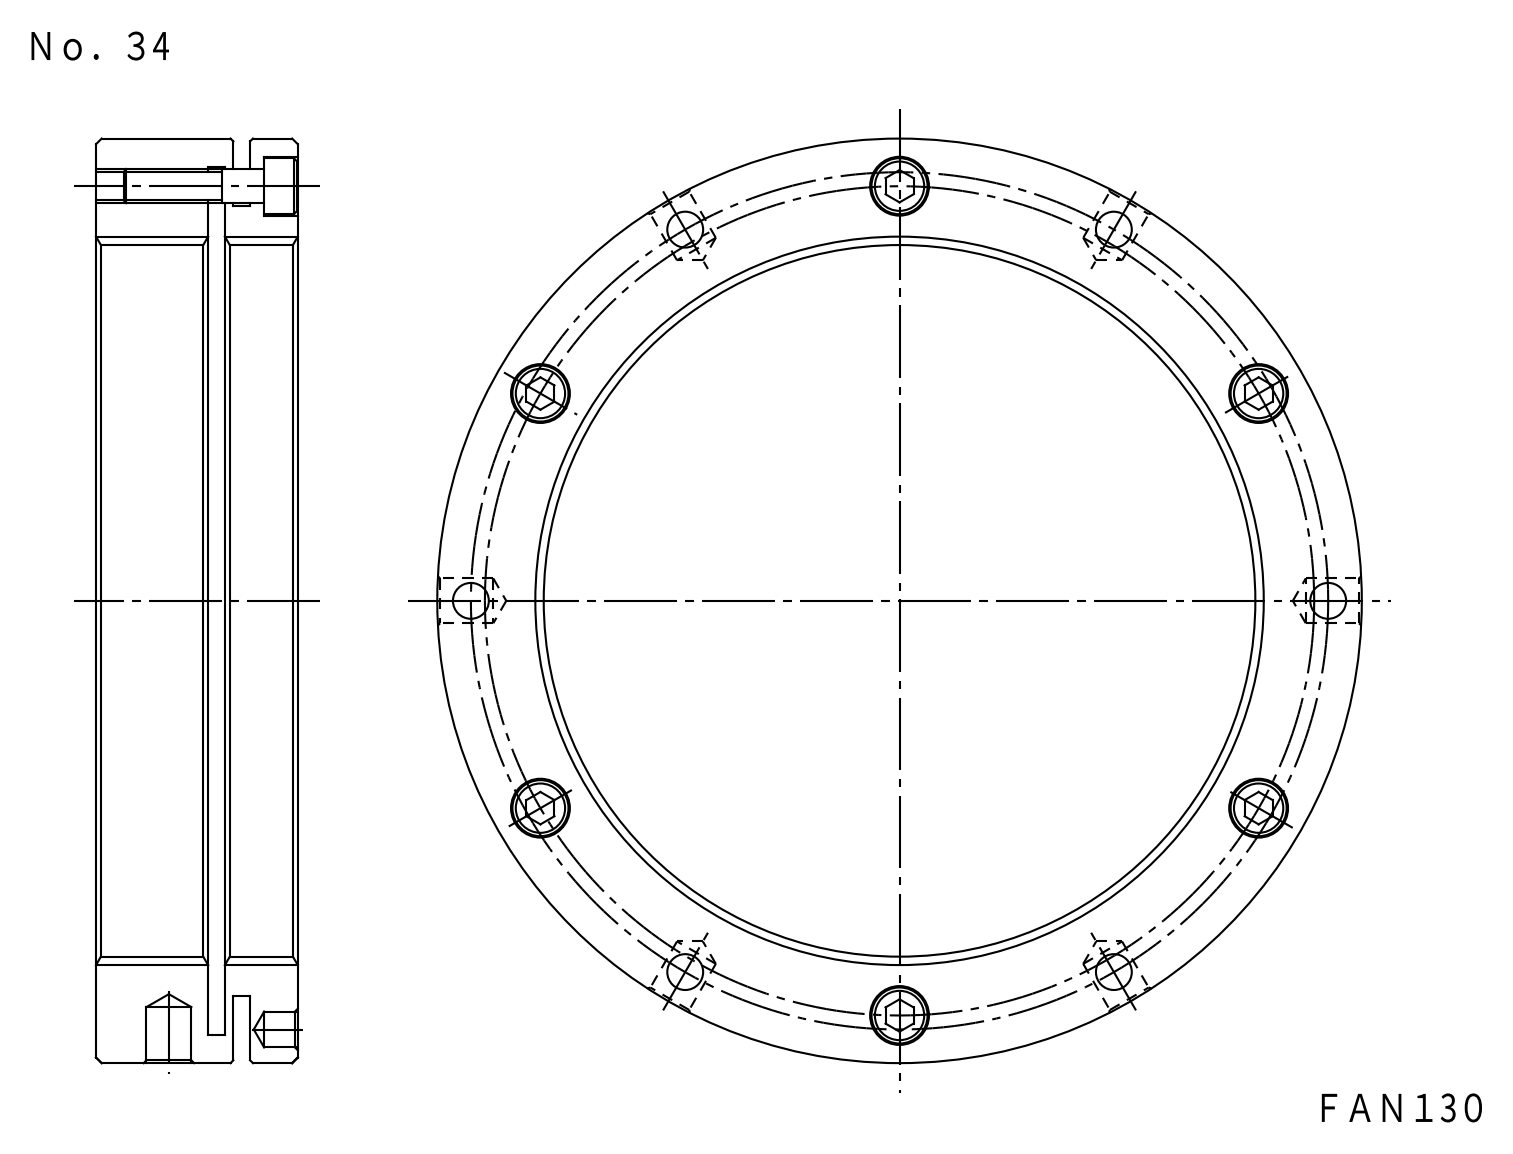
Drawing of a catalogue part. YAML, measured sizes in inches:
part_name: "FKD FAN130; M6X25_default"
step_written_by: "SolidWorks 2012 (CONFIG_CONTROL_DESIGN)"
units: inches
bodies: {solids: 7, faces: 204, planar: 72, cylindrical: 108, other: 24}
overall_size: [6.496, 6.496, 1.417]
volume: 15.46
surface_area: 127.7
round_holes:
  - {diameter: 0.194, count: 6}
  - {diameter: 0.252, count: 6}
  - {diameter: 0.268, count: 6}
  - {diameter: 0.433, count: 6}
  - {diameter: 0.315, count: 3}
  - {diameter: 5.118, count: 1}
  - {diameter: 6.102, count: 1}
round_bosses_or_shafts:
  - {diameter: 0.394, count: 6}
  - {diameter: 0.236, count: 6}
  - {diameter: 6.496, count: 1}
  - {diameter: 5.551, count: 1}
face_to_face_distances: [0.118, 0.177, 1.417, 0.965, 0.453, 1.083, 0.335, 0.787, 0.295, 0.63]
hole_center_spacings: [1.537, 2.913, 3.012, 4.19, 5.724, 5.217, 4.191, 5.046]
